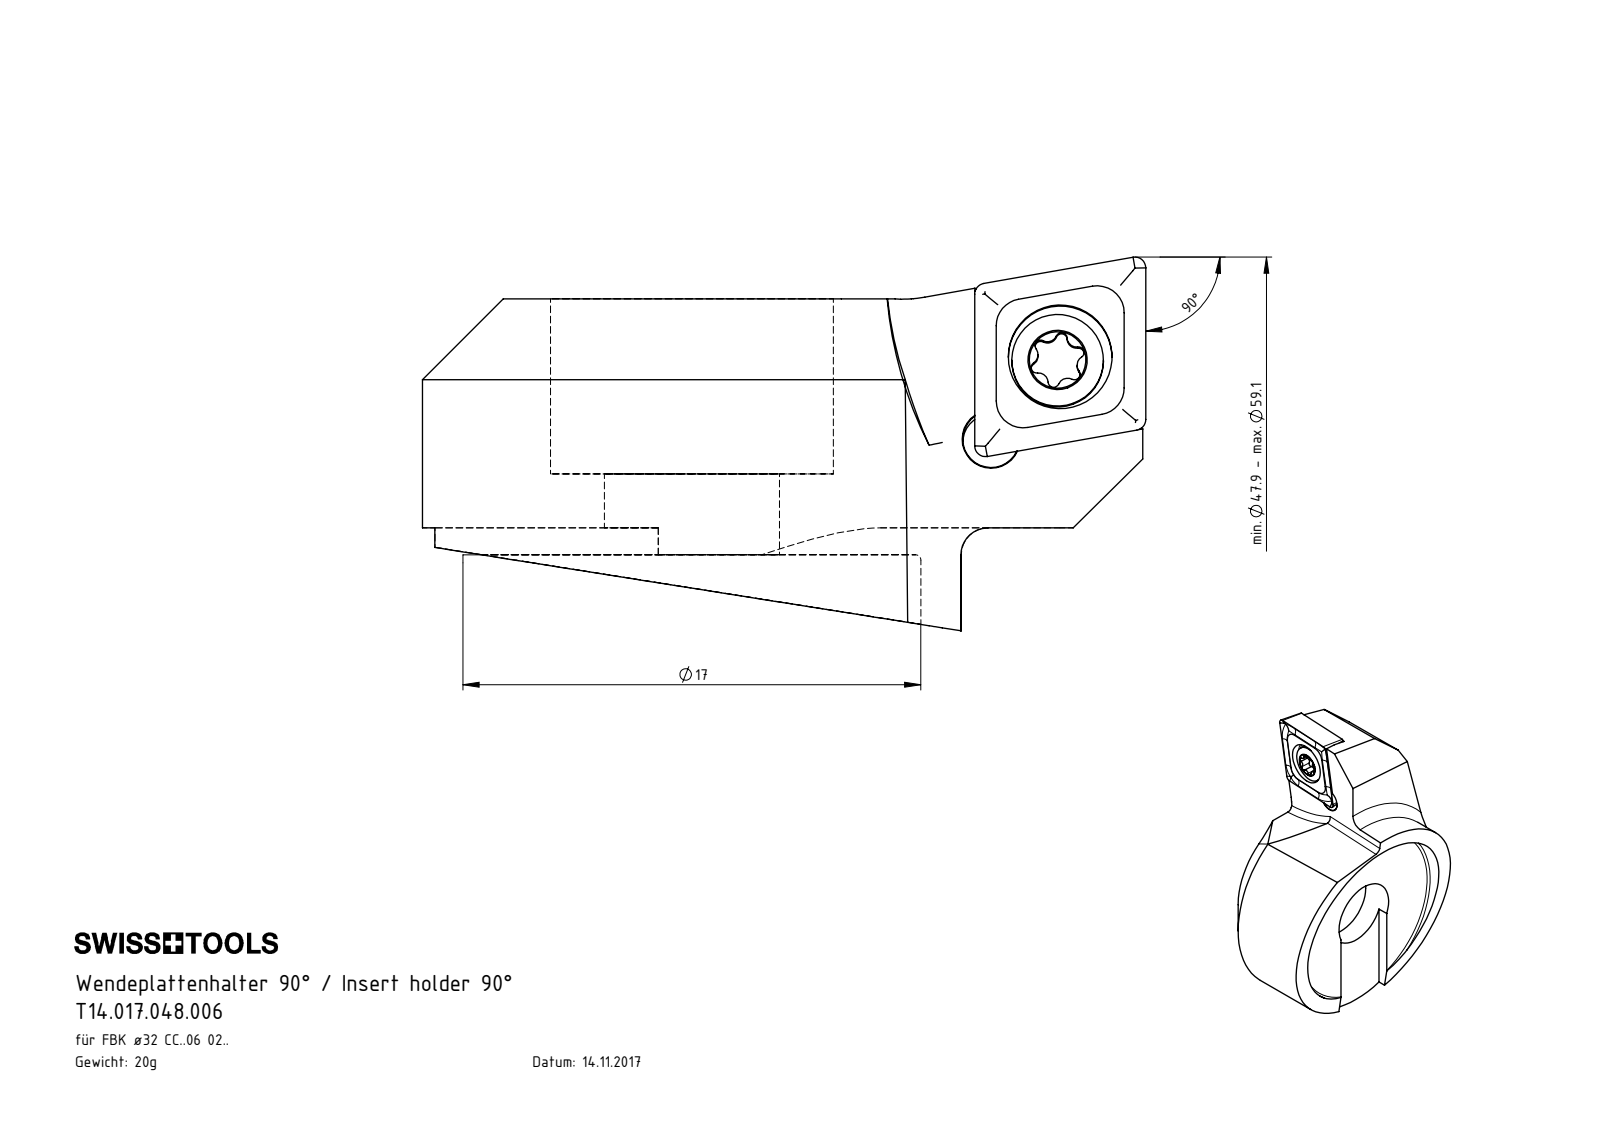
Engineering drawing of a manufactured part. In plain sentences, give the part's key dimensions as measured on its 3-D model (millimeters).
The part is named "F32.WCA.001.011; WCA-ER2.001.006_A; CCMT060204; F32-WCA.001.011_C_fertigbearbeitet". Its 3-D file was written by "SolidWorks 2017 (AUTOMOTIVE_DESIGN)". It is 3 solids with 104 faces: 38 planar, 26 cylindrical and 40 other. Overall it measures 26.85 by 20 by 13.87 millimeters. Its volume is 2 543 cubic millimeters and its surface area 1 915 square millimeters. Round holes: 1 of diameter 2.05, 1 of diameter 2.1, 1 of diameter 2.8, 1 of diameter 3.85, 1 of diameter 6.5, 1 of diameter 10.5. Round bosses or shafts: 1 of diameter 20, 1 of diameter 3.4, 1 of diameter 2.5. Partial cylindrical surfaces (rounded edges, fillets, slot ends): 6 of radius 0.21, 5 of radius 0.36, 2 of radius 0.5, 1 of radius 0.36, 1 of radius 5, 1 of radius 8.5, 1 of radius 15. The main face-to-face distances are 1, 8.5, 9.5, 6.5, 2, 3, 2.28, 2.27, 2.38, 2.39. The hole center spacings are 3.84, 3.99.
